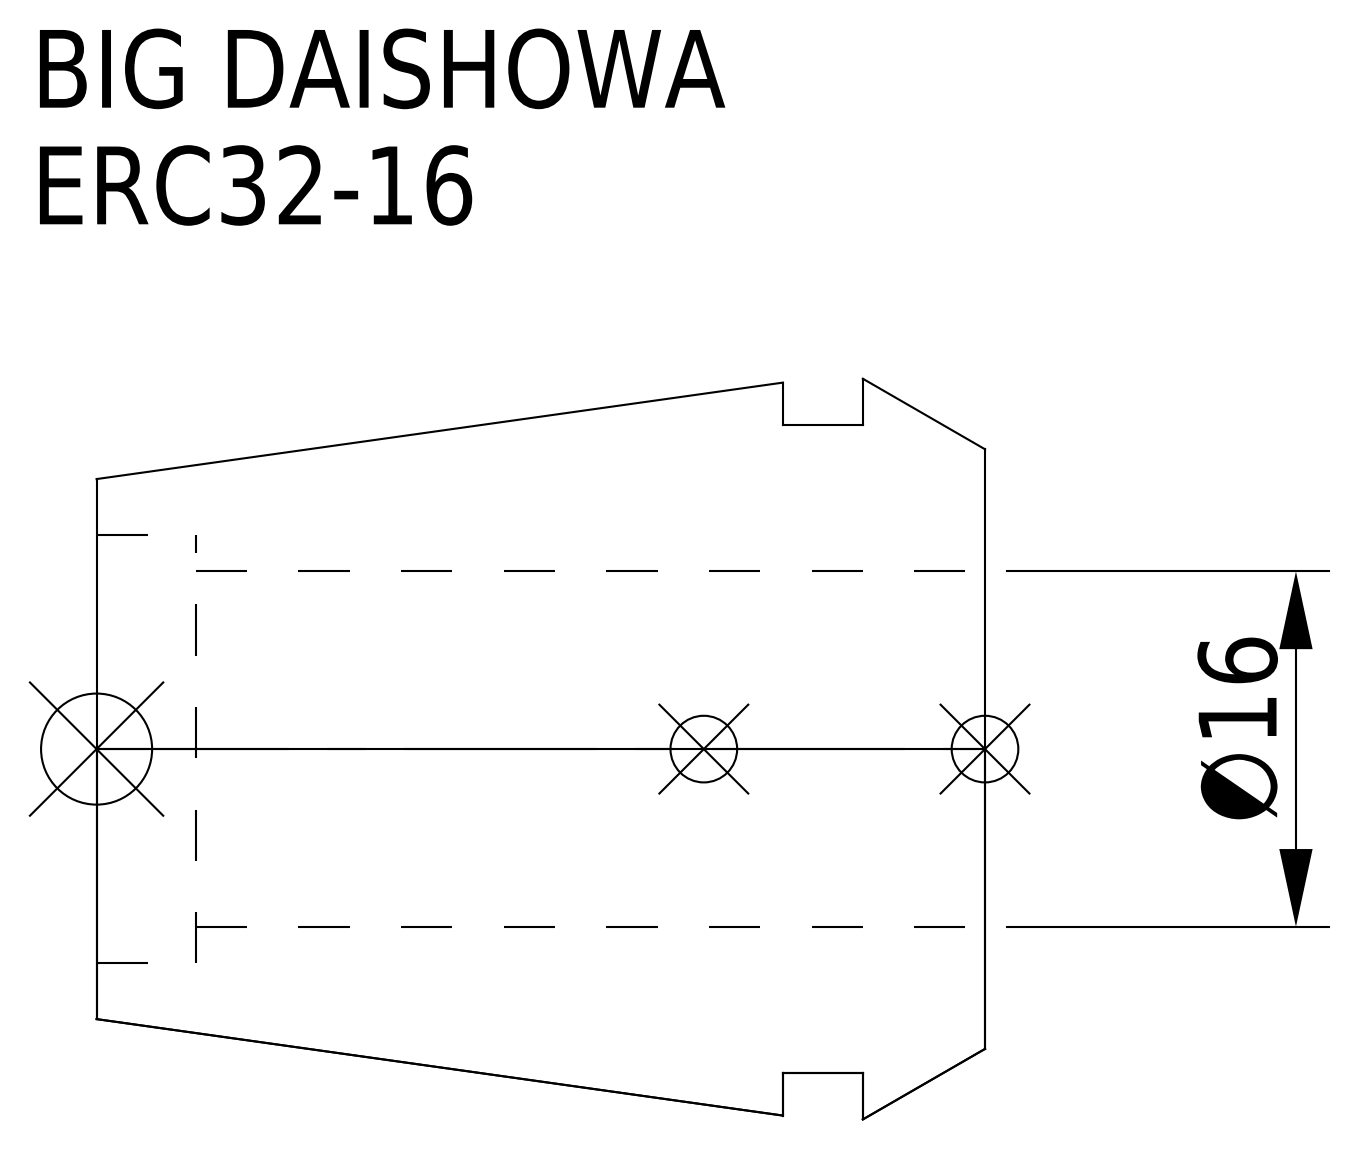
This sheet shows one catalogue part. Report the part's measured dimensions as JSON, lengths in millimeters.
{"part_name": "ERC32-16", "step_written_by": "CREO PARAMETRIC BY PTC INC, 2016380 (AUTOMOTIVE_DESIGN)", "units": "millimeters", "bodies": {"solids": 1, "faces": 15, "planar": 5, "cylindrical": 6, "other": 4}, "overall_size": [40, 33.35, 33.35], "volume_mm3": 17991, "surface_area_mm2": 6823, "round_holes": [[16, 1], [19.3, 1]], "round_bosses_or_shafts": [[29.2, 1]], "face_to_face_distances": [5.5, 9.1, 3.6, 40, 34.5, 30.9, 35.53, 30.03, 26.43, 4.47]}
